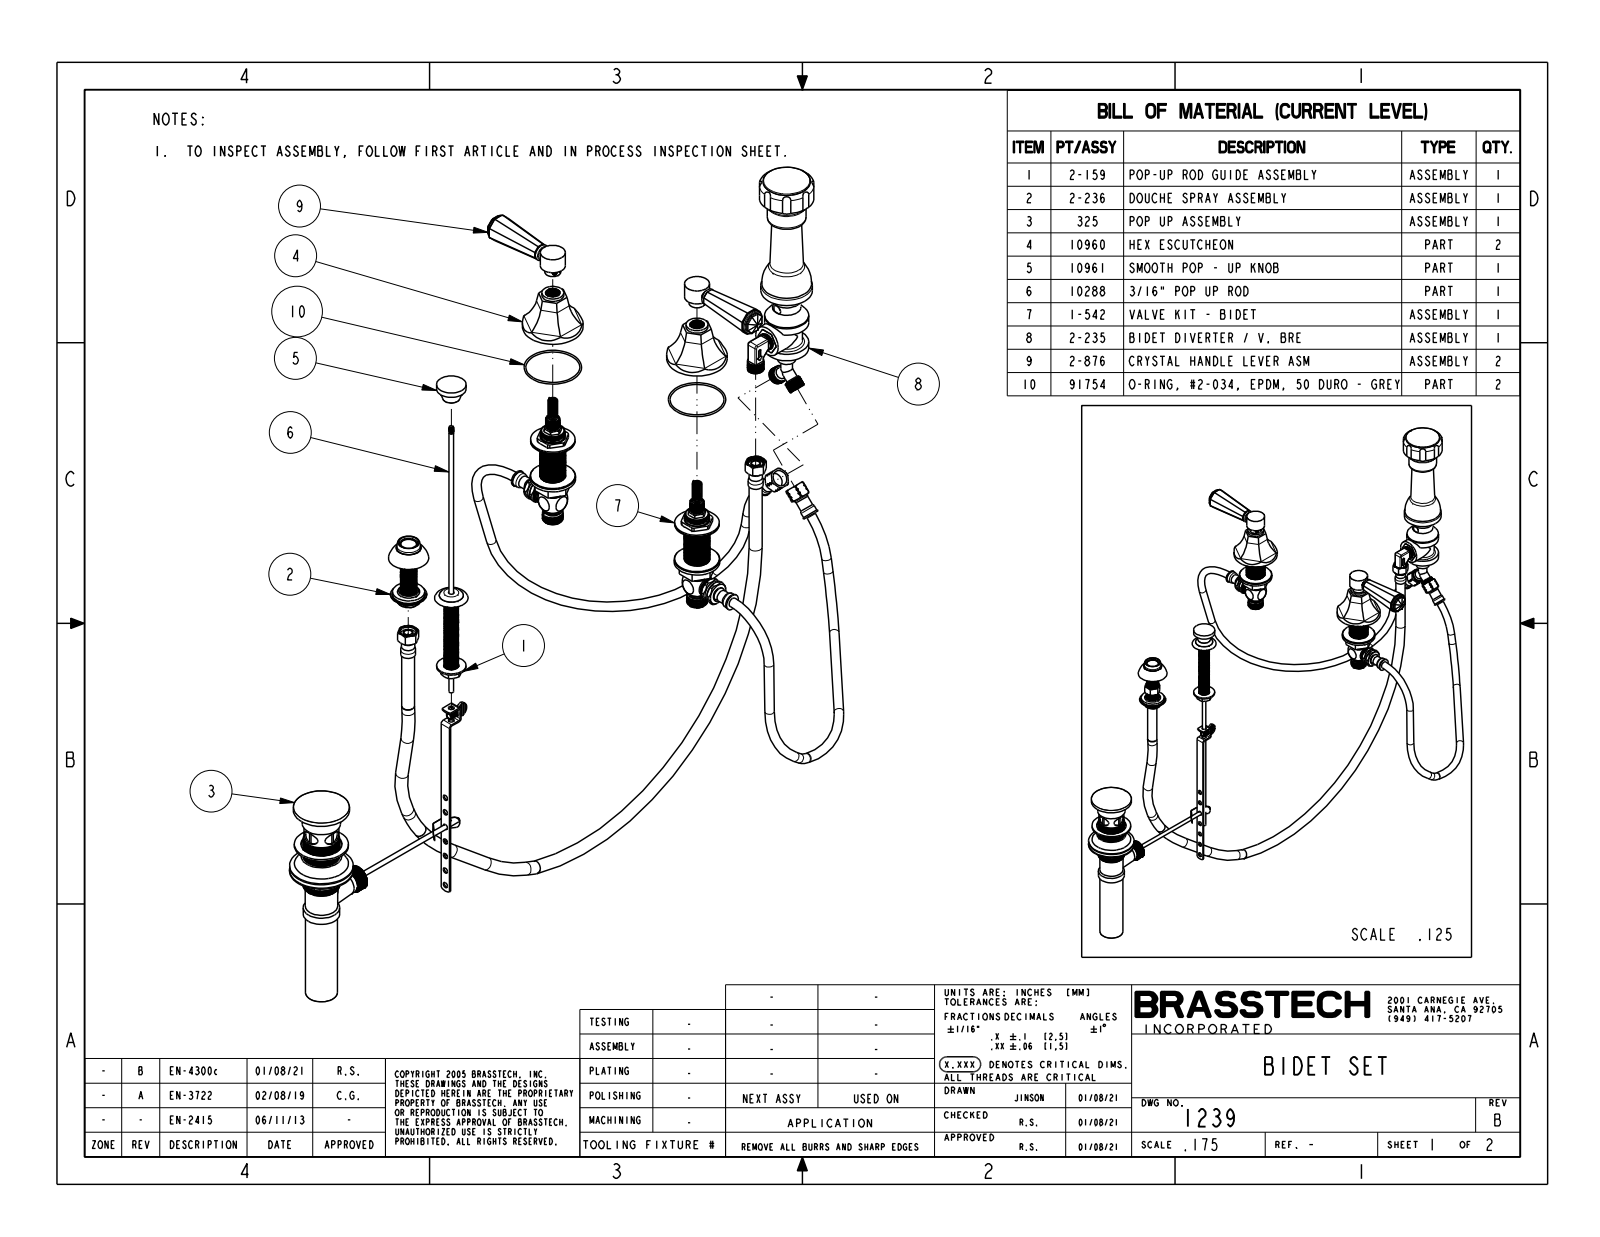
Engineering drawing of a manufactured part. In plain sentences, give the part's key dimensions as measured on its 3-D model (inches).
The part is named "1239". Its 3-D file was written by "CREO PARAMETRIC BY PTC INC, 2018400 (CONFIG_CONTROL_DESIGN)". It is 5 solids with 399 faces: 175 planar, 130 cylindrical and 94 other. Overall it measures 22.857 by 14.716 by 5.353 inches. Its volume is 23.71 cubic inches and its surface area 103 square inches. Round holes: 1 of diameter 0.385, 1 of diameter 0.625, 1 of diameter 0.792, 1 of diameter 0.94. Round bosses or shafts: 3 of diameter 0.98, 2 of diameter 2.375, 2 of diameter 0.86, 2 of diameter 0.625, 1 of diameter 2.025, 1 of diameter 1.52, 1 of diameter 1.16, 1 of diameter 0.925. Partial cylindrical surfaces (rounded edges, fillets, slot ends): 40 of radius 0.03, 12 of radius 1.541, 8 of radius 0.21, 1 of radius 0.357, 1 of radius 1.077. The main face-to-face distances are 0.169, 0.169, 3.928, 1.957, 3.468, 1.511, 1.527, 0.43, 1.941, 1.647.
